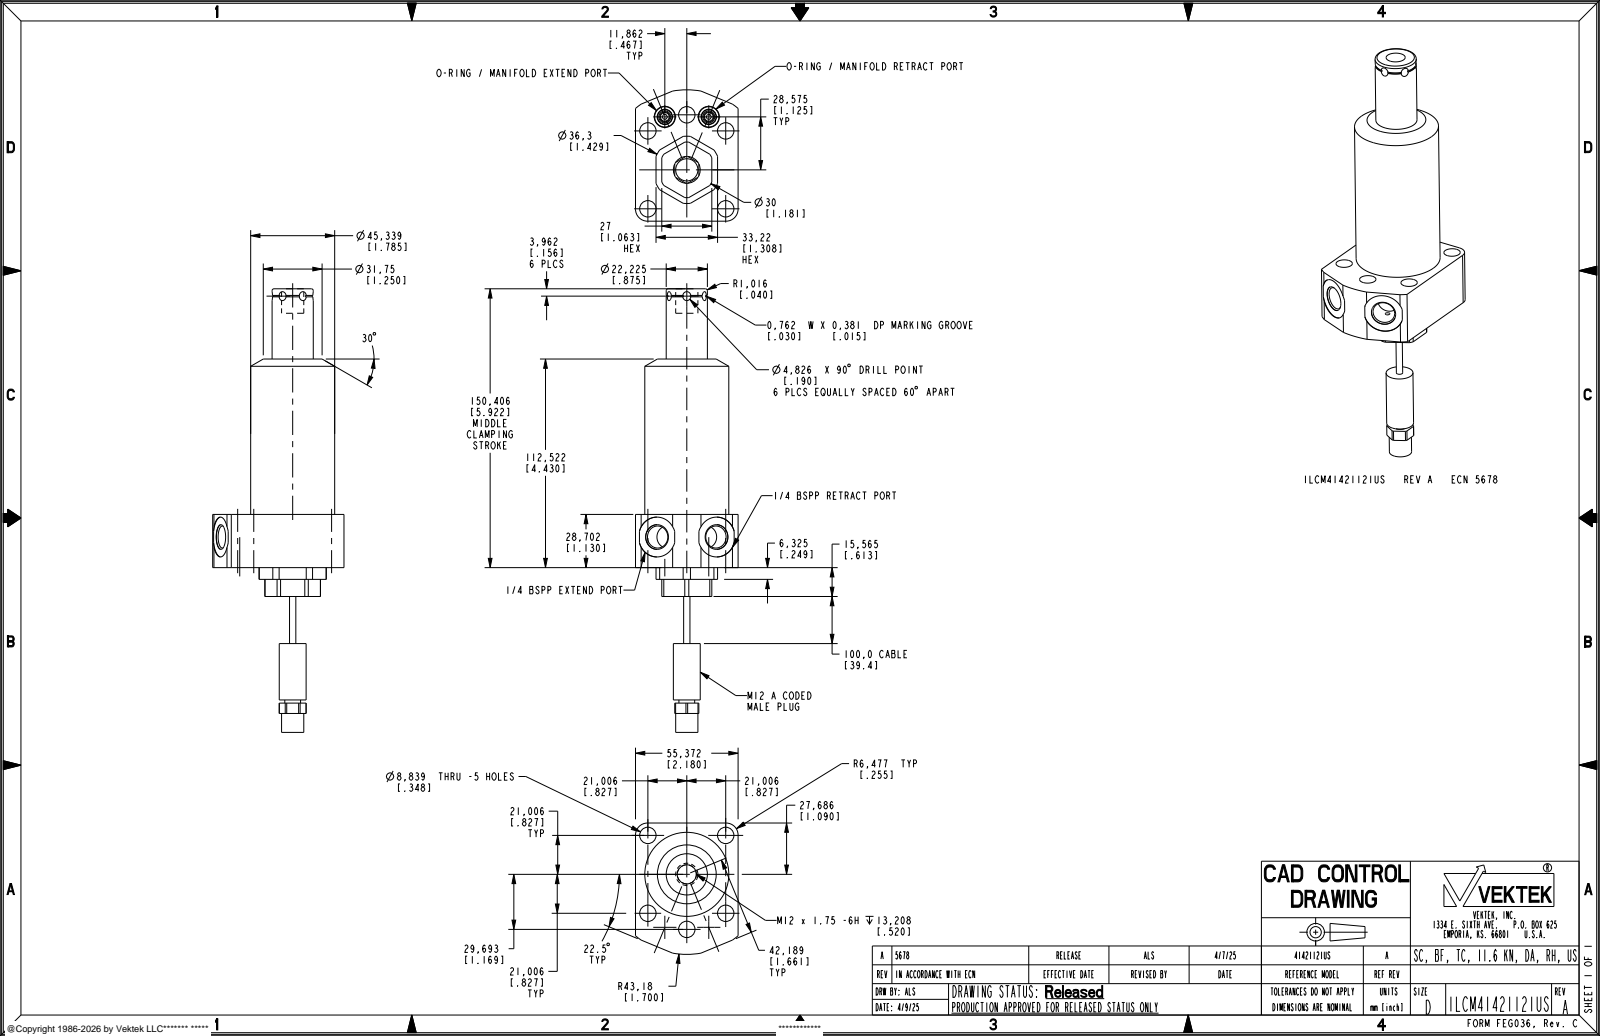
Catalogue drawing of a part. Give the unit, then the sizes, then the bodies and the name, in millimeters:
Units: millimetres
Overall size (bounding box): 239.28 × 86.87 × 63.37
Round holes (diameter × count): ⌀8.84 ×5, ⌀2.49 ×2, ⌀6.5 ×2, ⌀11.4 ×2, ⌀11.89 ×2, ⌀13.31 ×2, ⌀21.5 ×2, ⌀10.31 ×1
Round bosses / shafts (diameter × count): ⌀5.49 ×2, ⌀45.34 ×1, ⌀22.23 ×1, ⌀14.5 ×1, ⌀11.99 ×1, ⌀11.99 ×1, ⌀8.51 ×1, ⌀3.4 ×1
Partial cylindrical surfaces — rounded edges, fillets, slot ends (radius × count): R6.48 ×2, R10.73 ×1, R15 ×1, R18.15 ×1, R43.18 ×1
Main face-to-face distances: 28.7, 55.38, 15.57, 44.27, 3.11, 30.11, 128.09, 112.52, 83.82, 27
Hole centre spacings: 29.71, 42.02, 11.87, 11.91, 22.73, 30.93, 33.73, 50.42
Volume: 259 680 mm³ · Surface area: 38 873 mm²
Bodies: 1 solid, 198 faces (79 planar, 85 cylindrical, 34 other)
Part name (STEP PRODUCT): ILCM41421121US
STEP written by: CREO PARAMETRIC BY PTC INC, 2021164 (AUTOMOTIVE_DESIGN)
